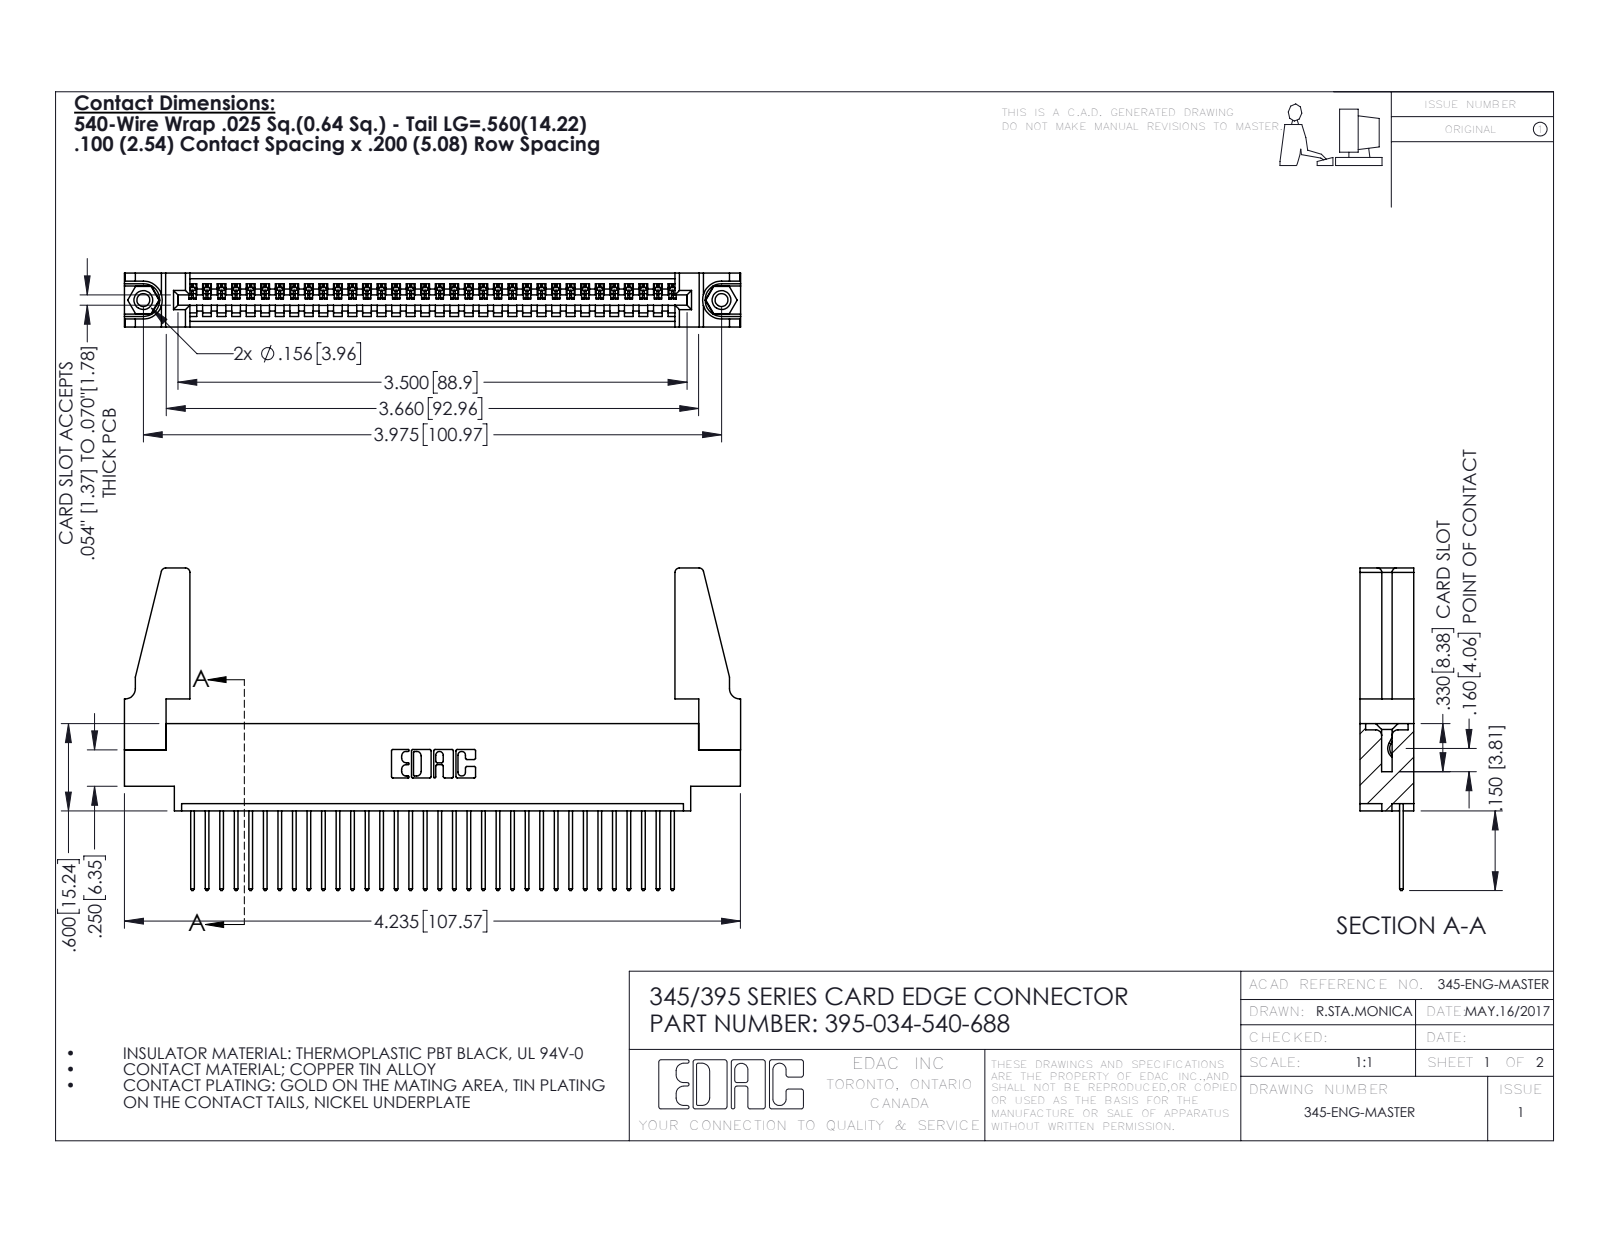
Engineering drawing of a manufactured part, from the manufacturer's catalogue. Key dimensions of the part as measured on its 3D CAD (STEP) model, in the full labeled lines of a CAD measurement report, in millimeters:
Part name (STEP PRODUCT): 345-250-001_345-250-001-102; 395-034-540-688; 345-220-078_345-220-088; 345-292-001_345-293-140 (+1 more)
STEP written by: SolidWorks 2016 (CONFIG_CONTROL_DESIGN)
Units: millimetres
Bodies: 39 solids, 2226 faces (1516 planar, 694 cylindrical, 16 other)
Overall size (bounding box): 107.6 × 56.3 × 9.4
Volume: 13 300 mm³ · Surface area: 16 880 mm²
Round holes (diameter × count): ⌀2.3 ×2, ⌀3.2 ×2, ⌀4 ×2, ⌀1.6 ×1
Round bosses / shafts (diameter × count): ⌀3.9 ×2
Partial cylindrical surfaces — rounded edges, fillets, slot ends (radius × count): R0.2 ×68, R0.3 ×68, R0.3 ×22, R0.8 ×8, R0.2 ×6, R0.8 ×6, R0.7 ×3, R0.8 ×2
Main face-to-face distances: 1.8, 9.4, 7.6, 2.5, 6.9, 0.6, 5.1, 5.7, 4.4, 3.8
Hole centre spacings: 6.9, 95, 101
